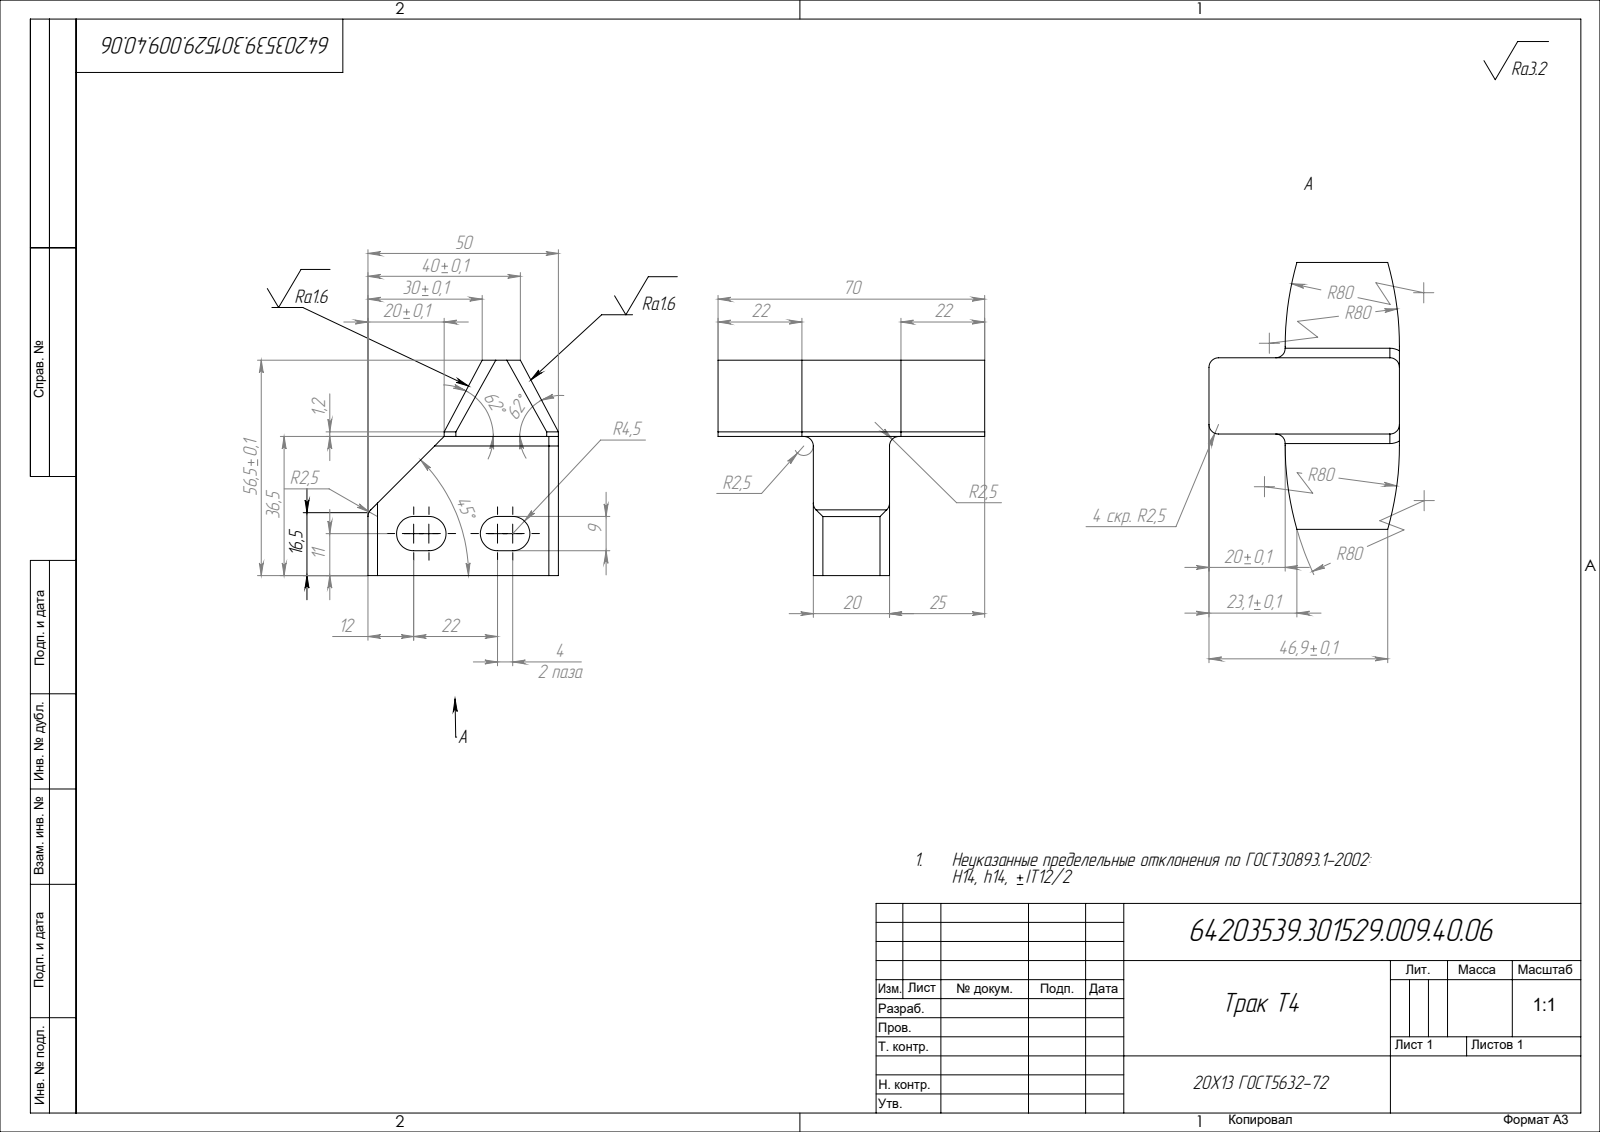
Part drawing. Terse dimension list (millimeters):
name: 64203539.301529.009.40.06 Трак Т4
written by: SolidWorks 2017 (CONFIG_CONTROL_DESIGN)
unit: mm
bodies: 1 solid, 39 faces (18 planar, 15 cylindrical, 6 other)
size: 70 × 56.5 × 50
volume: 55 374 mm³; area: 12 496 mm²
rounds: 7× R2.5, 4× R4.5, 4× R80
face distances: 20, 36.5, 56.5, 25, 45, 50, 70, 30, 15.5, 21
